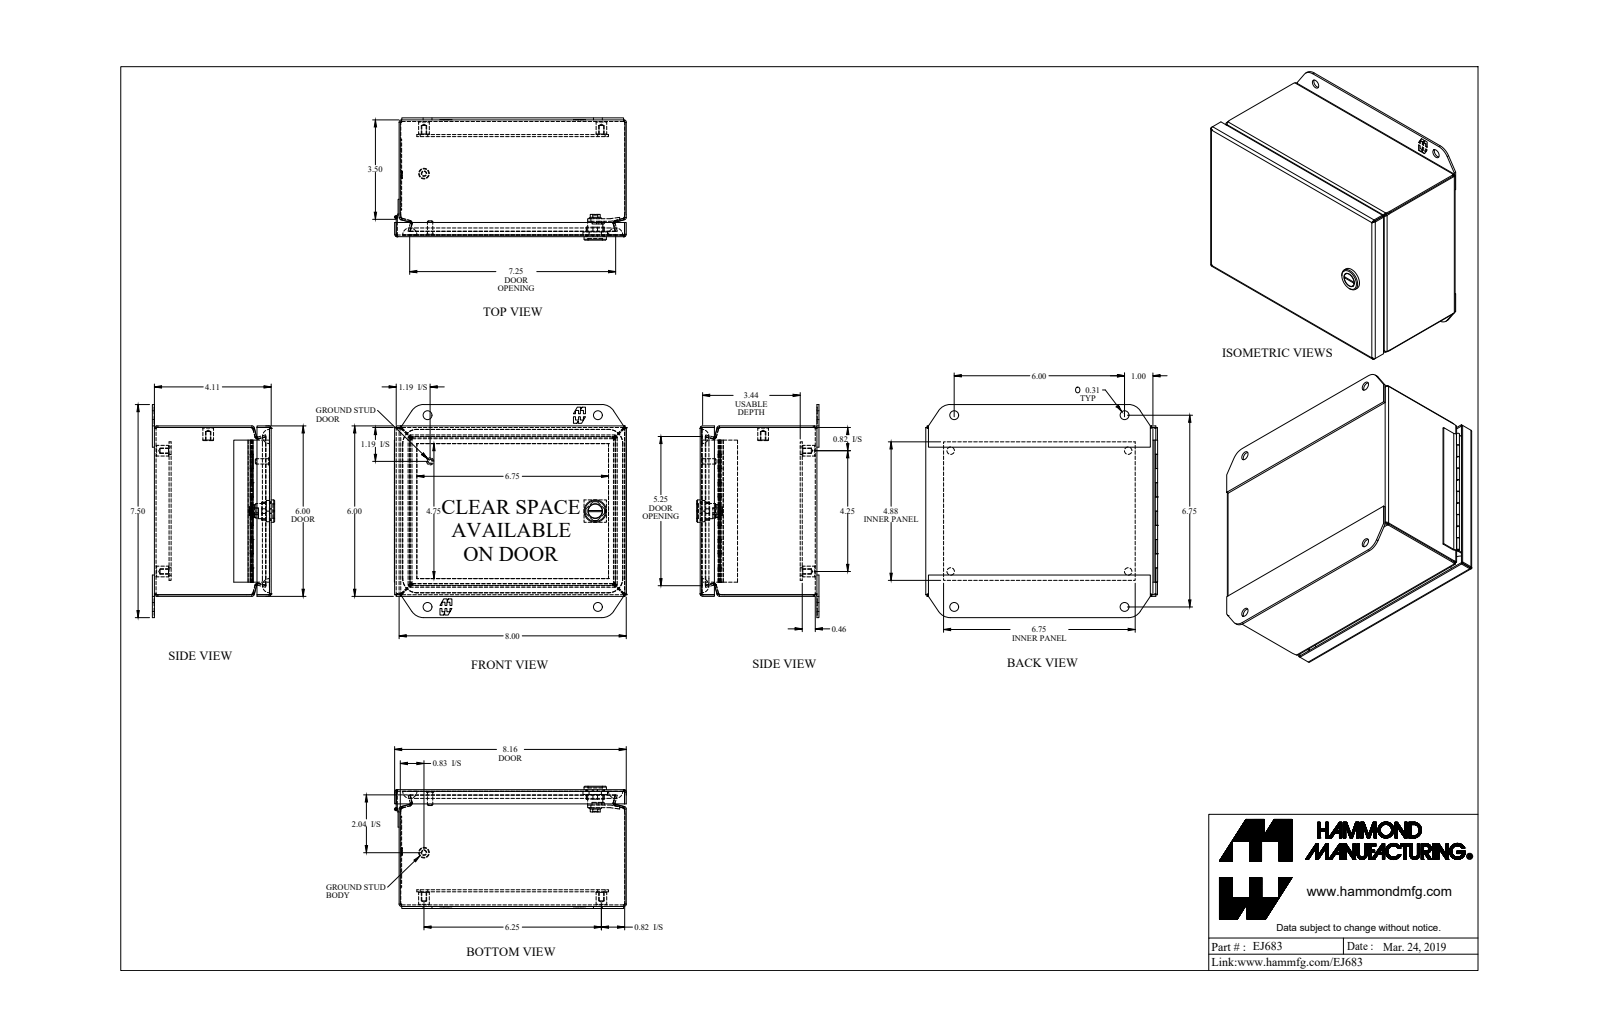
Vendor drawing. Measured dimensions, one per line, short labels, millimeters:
name: EJ683_Default
written by: SolidWorks 2019 (CONFIG_CONTROL_DESIGN)
unit: mm
bodies: 16 solids, 611 faces (345 planar, 174 cylindrical, 92 other)
size: 207.4 × 190.5 × 109.3
volume: 322 500 mm³; area: 414 300 mm²
holes: 5× ⌀4, 4× ⌀6.7, 4× ⌀8, 1× ⌀1.3, 1× ⌀13.1
bosses: 5× ⌀9.5, 1× ⌀20, 1× ⌀13.6, 1× ⌀12.6, 1× ⌀11, 1× ⌀6.4, 1× ⌀4.8, 1× ⌀2.5
rounds: 16× R0.7, 16× R2.2, 10× R7.1, 4× R6.4, 4× R12.7, 4× R12.7, 2× R1.5, 2× R13.7
face distances: 1.4, 103, 151, 1.8, 15, 104.4, 101.5, 201.8, 11.7, 13.1
hole spacings: 31.9, 139.7, 54.3, 108, 158.8, 209.1, 85.8, 152.4
